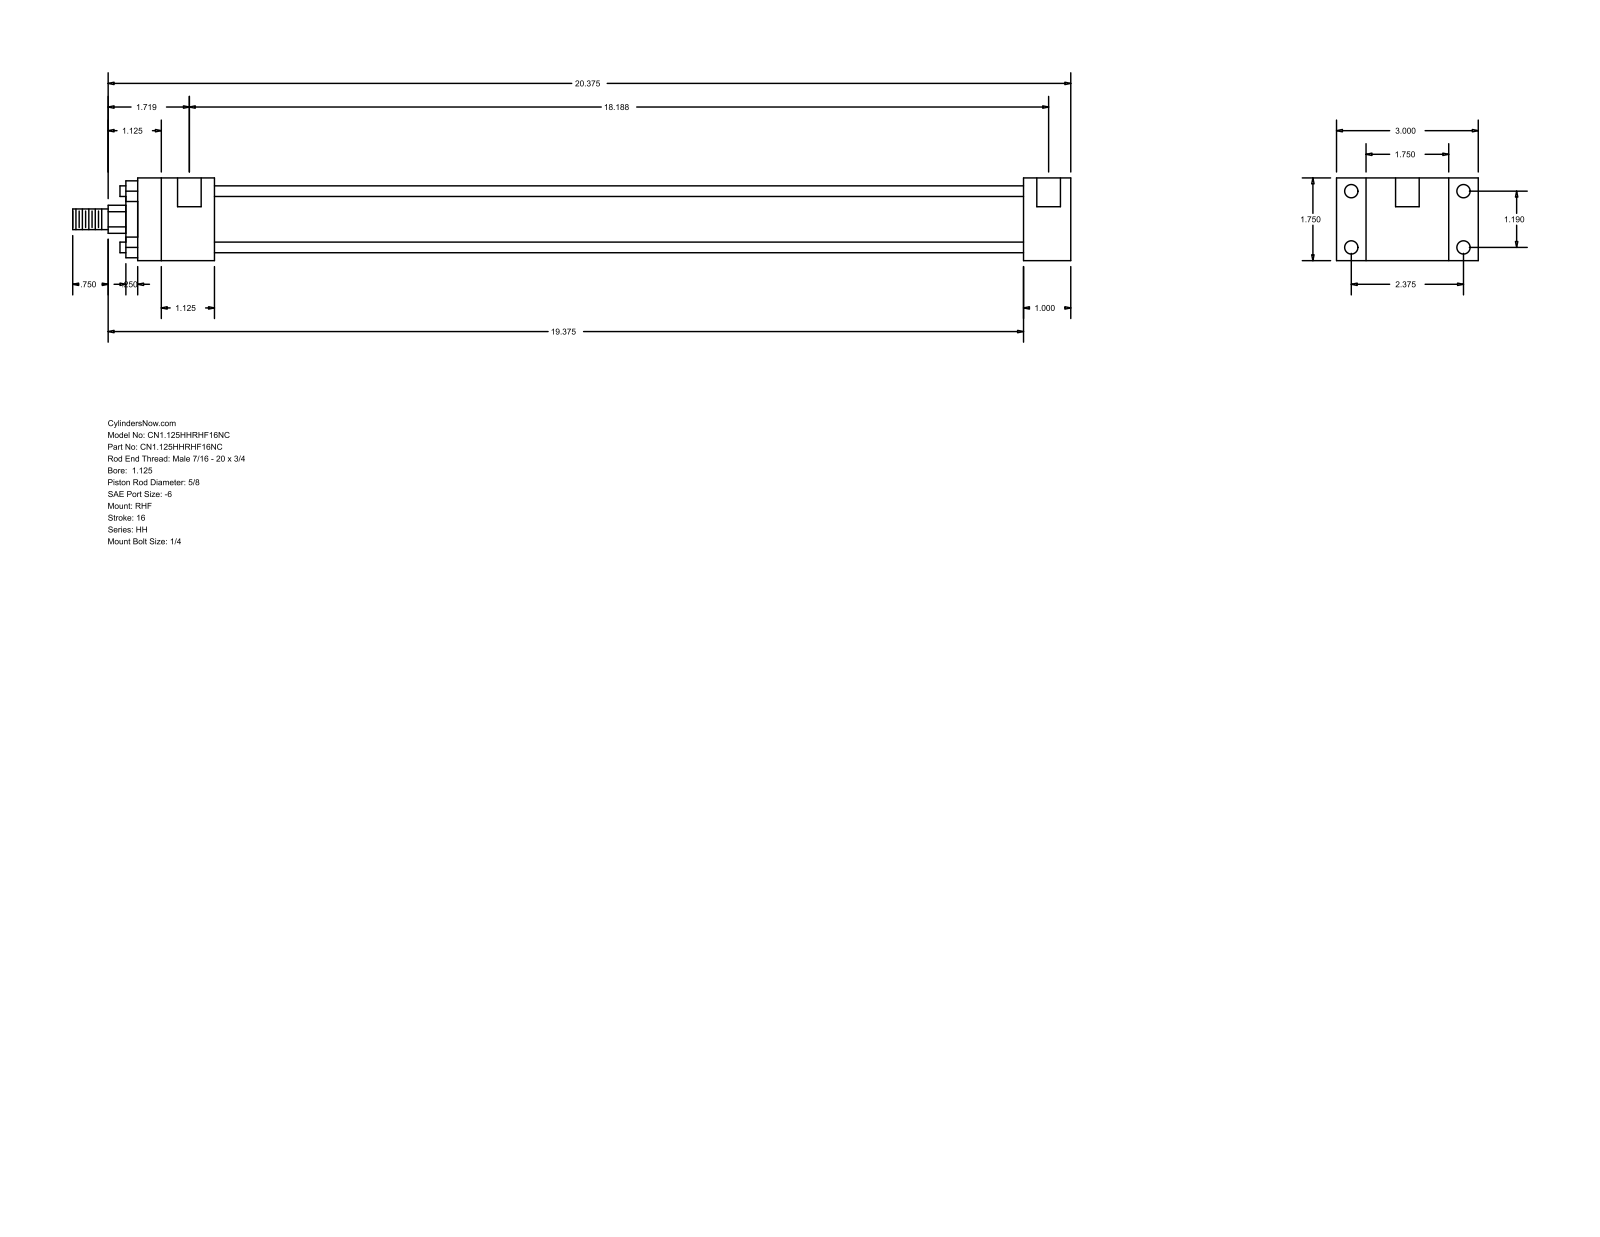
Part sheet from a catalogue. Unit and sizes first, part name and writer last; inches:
Units: inches
Overall size (bounding box): 21.125 × 3 × 1.75
Round holes (diameter × count): ⌀0.219 ×4, ⌀0.281 ×4, ⌀0.5 ×2
Round bosses / shafts (diameter × count): ⌀0.225 ×4, ⌀1.375 ×1, ⌀1.125 ×1, ⌀0.625 ×1, ⌀0.437 ×1
Partial cylindrical surfaces — rounded edges, fillets, slot ends (radius × count): R0.297 ×1
Main face-to-face distances: 1.75, 0.625, 1, 2.375, 3, 17.125, 18.125, 1.625, 18.75, 19.75
Hole centre spacings: 1.19, 2.375, 2.656, 18.063, 0.125, 18.187
Bodies: 0 solids, 88 faces (60 planar, 28 cylindrical, 0 other)
Part name (STEP PRODUCT): HH_RHF__0112_0.625
STEP written by: GSSL Pune (CONFIG_CONTROL_DESIGN)
